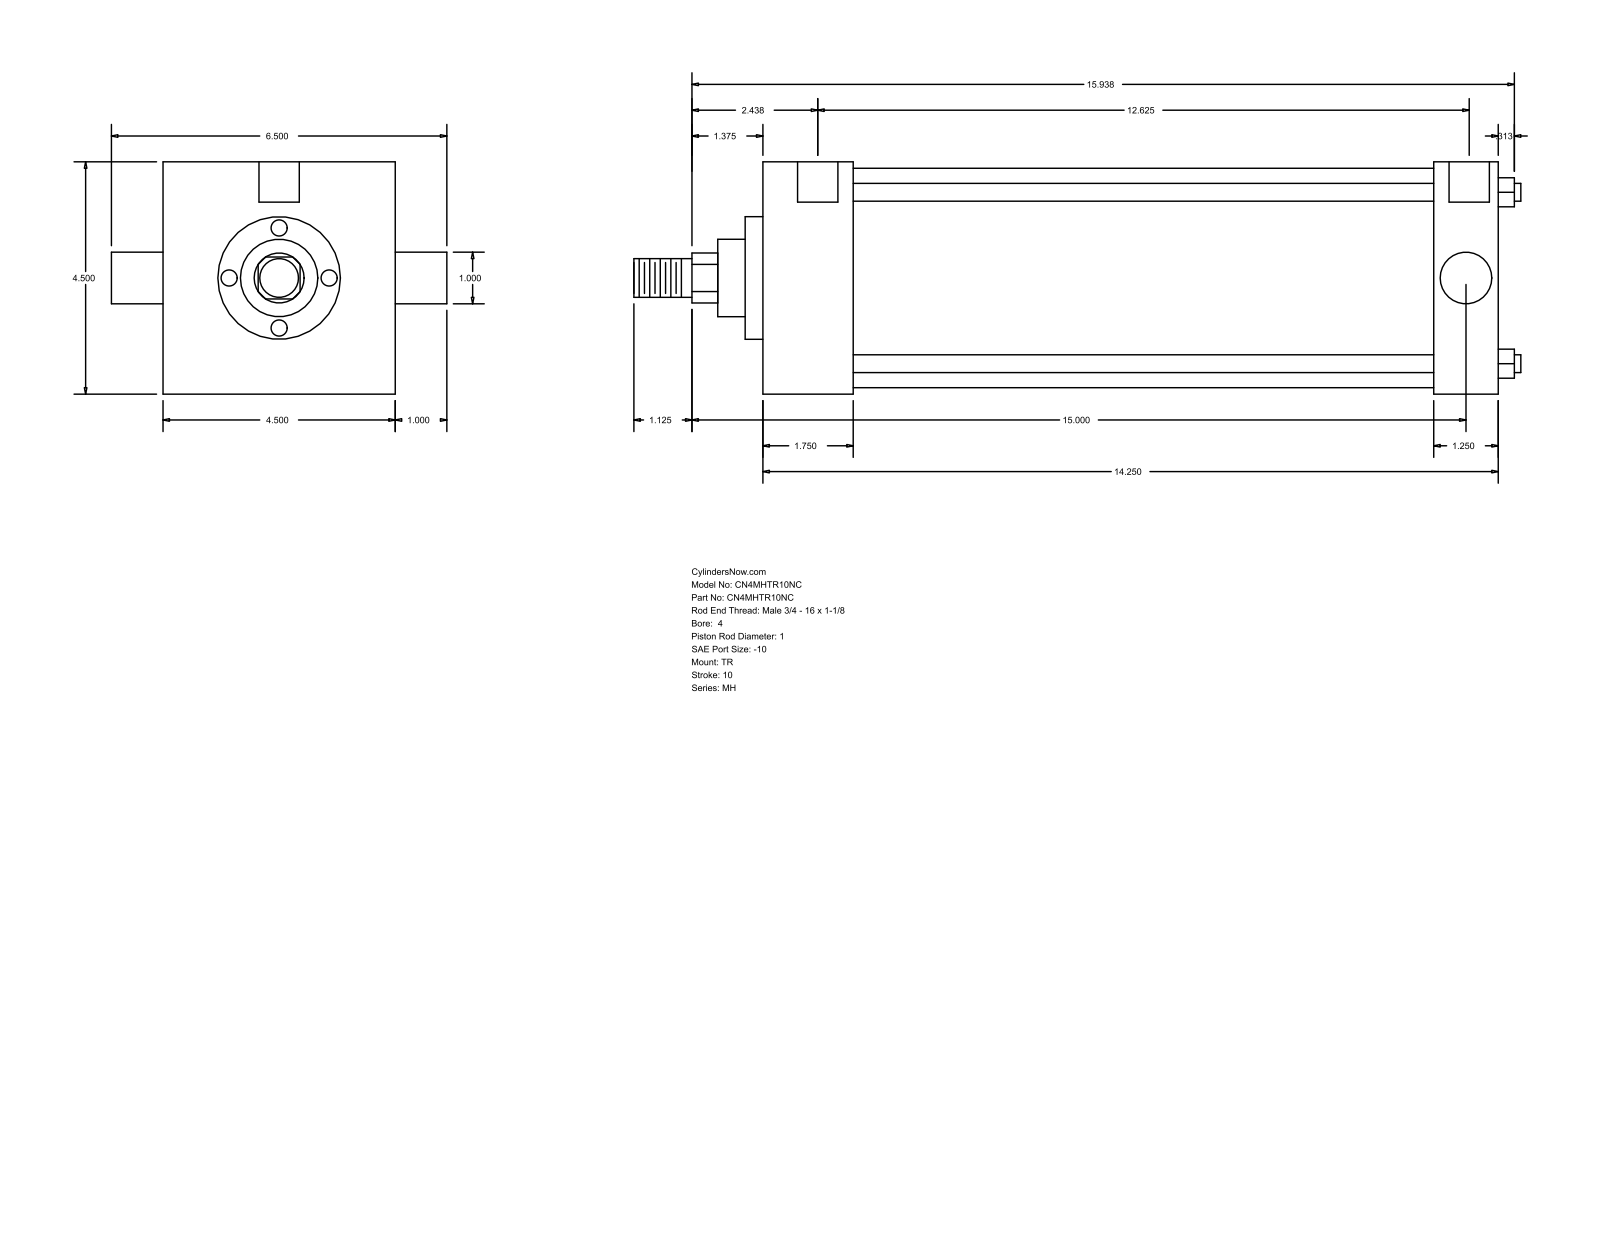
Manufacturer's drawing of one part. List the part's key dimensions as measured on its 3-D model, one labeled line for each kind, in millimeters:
Part name (STEP PRODUCT): MH_TR__0400_1
STEP written by: GSSL Pune (CONFIG_CONTROL_DESIGN)
Units: millimetres
Bodies: 0 solids, 86 faces (61 planar, 25 cylindrical, 0 other)
Overall size (bounding box): 436.56 × 165.1 × 114.3
Round holes (diameter × count): ⌀8.73 ×3, ⌀19.84 ×2
Round bosses / shafts (diameter × count): ⌀8.76 ×4, ⌀25.4 ×2, ⌀107.95 ×1, ⌀60.33 ×1, ⌀38.1 ×1, ⌀19.05 ×1
Partial cylindrical surfaces — rounded edges, fillets, slot ends (radius × count): R12.29 ×1
Main face-to-face distances: 114.3, 361.96, 44.46, 317.5, 330.2, 285.74, 31.76, 8.73, 53.19, 338.93
Hole centre spacings: 1.58, 1.59, 320.68, 322.26, 322.27, 323.85
